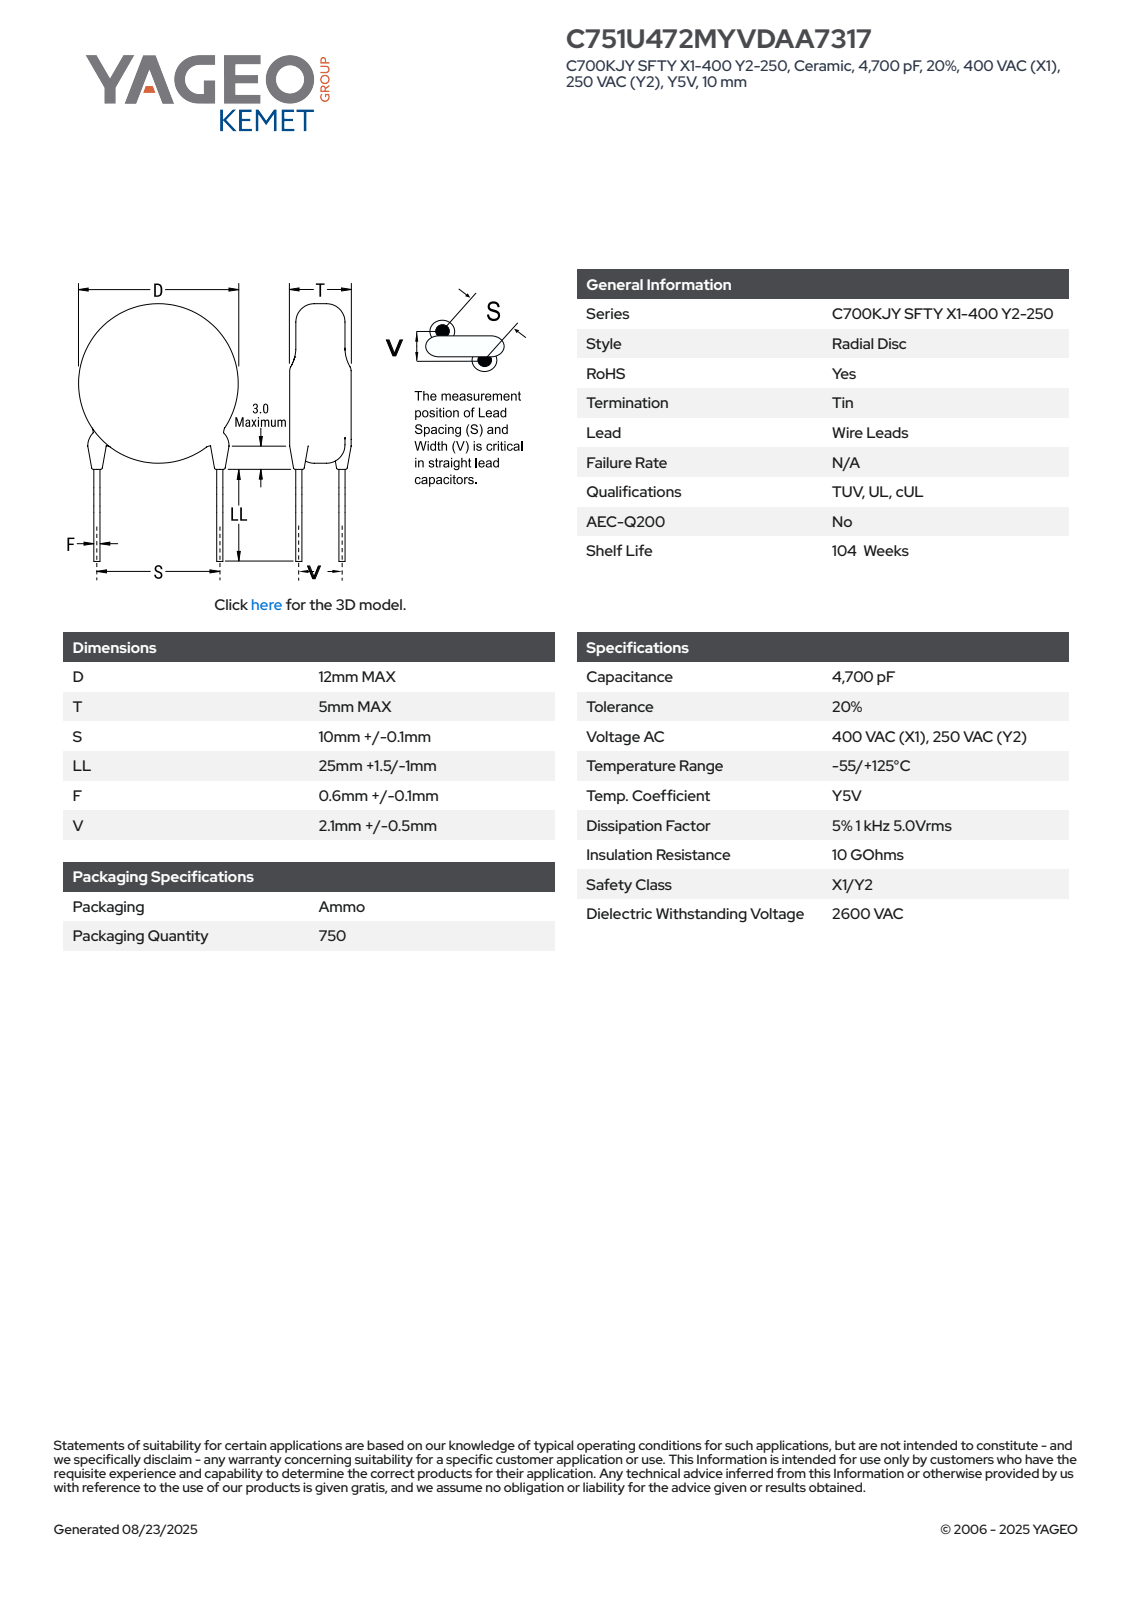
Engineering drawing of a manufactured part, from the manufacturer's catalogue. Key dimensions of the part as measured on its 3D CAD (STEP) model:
Part name (STEP PRODUCT): CCD_KST_12X5_D12T5S10.1LL26.5F0.7V2.1
STEP written by: SolidWorks 2021 (AUTOMOTIVE_DESIGN)
Units: millimetres
Bodies: 4 solids, 80 faces (63 planar, 13 cylindrical, 4 other)
Overall size (bounding box): 39.25 × 12 × 5
Volume: 578 mm³ · Surface area: 534 mm²
Round bosses / shafts (diameter × count): ⌀1.2 ×4, ⌀0.7 ×2, ⌀12 ×1
Main face-to-face distances: 5, 26.5, 34.16, 7.66, 32.8, 6.3, 1.36, 0.37, 1.1, 5.55
